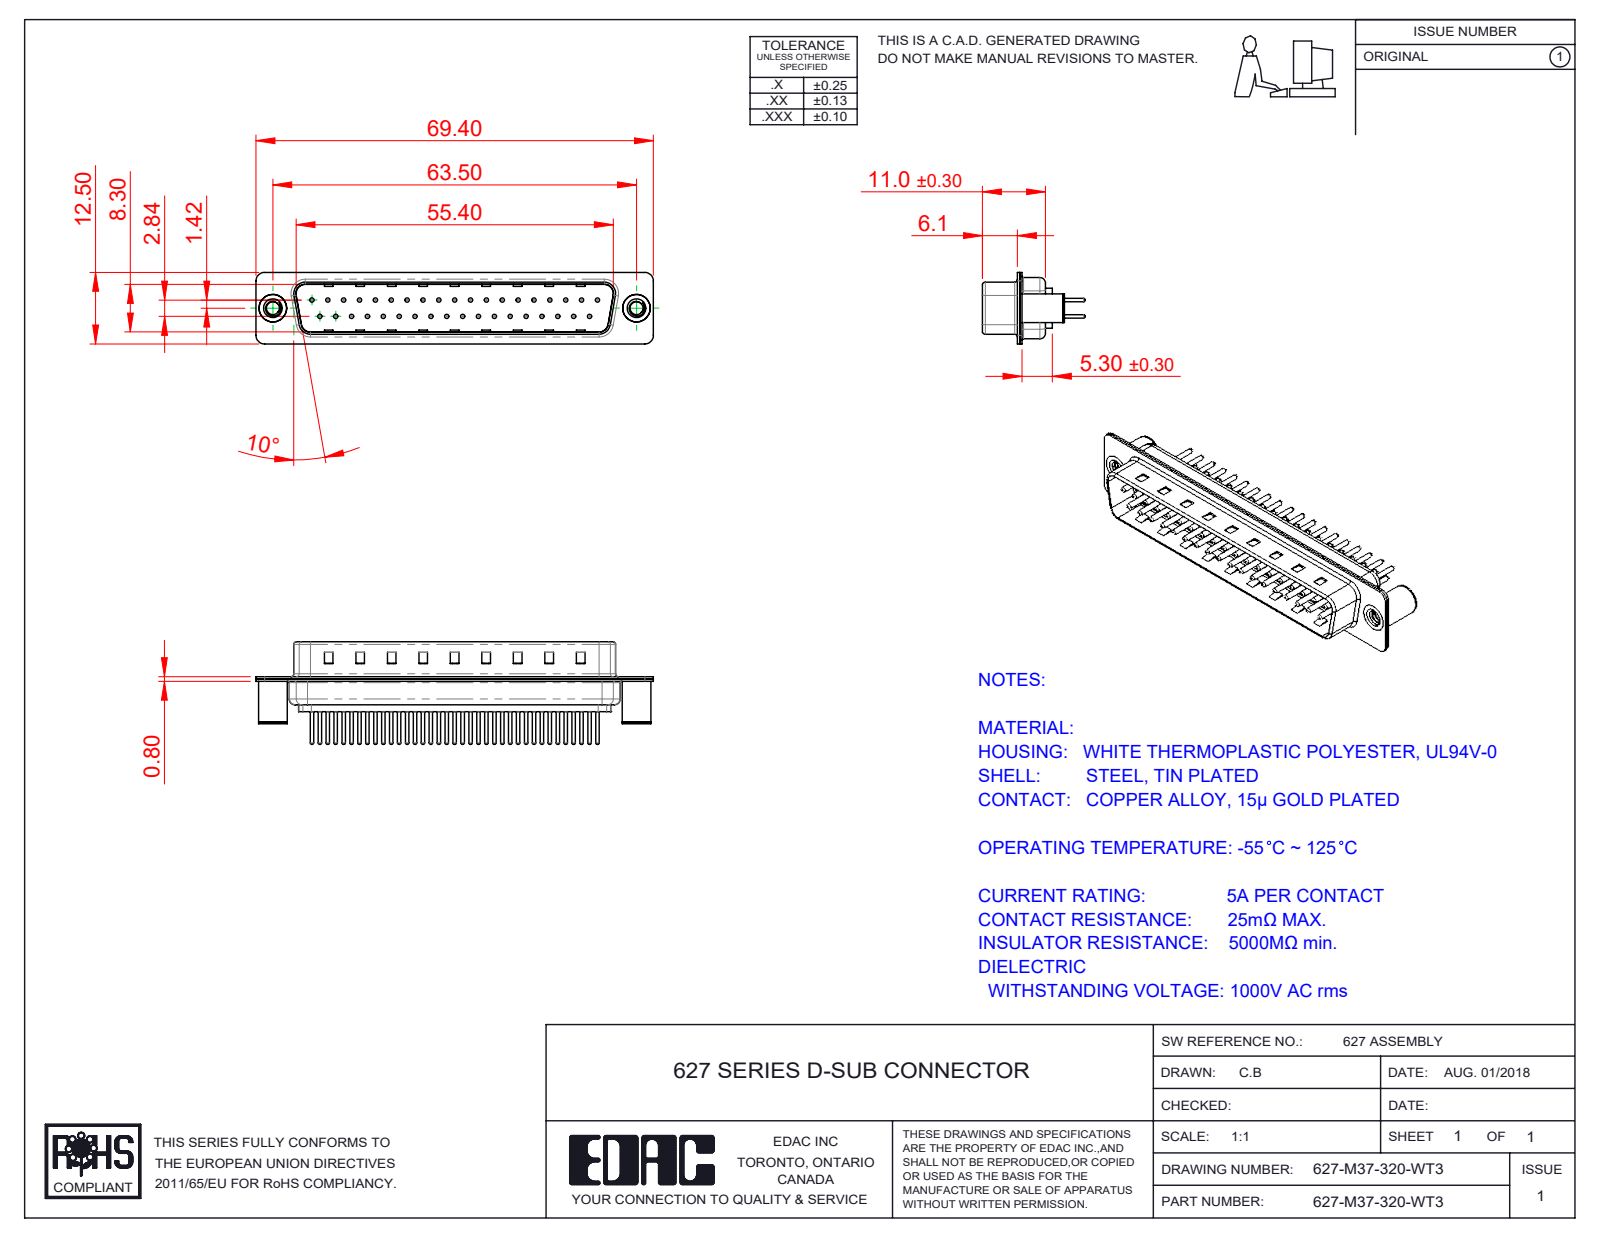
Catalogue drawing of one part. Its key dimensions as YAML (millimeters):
part_name: "627M Contact Row 1_20; 627M Shell Front_37 Contacts; 627M Contact Row 2_20; 627M Shell Rear_37 Contacts (+3 more)"
step_written_by: "SolidWorks 2020 (CONFIG_CONTROL_DESIGN)"
units: millimeters
bodies: {solids: 42, faces: 1815, planar: 462, cylindrical: 683, other: 670}
overall_size: [69.4, 17.9, 12.5]
volume: 3891
surface_area: 9528
round_holes:
  - {diameter: 0.75, count: 37}
  - {diameter: 1.6, count: 37}
  - {diameter: 2, count: 37}
  - {diameter: 2.26, count: 2}
  - {diameter: 3.26, count: 2}
  - {diameter: 4, count: 2}
  - {diameter: 4.8, count: 2}
round_bosses_or_shafts:
  - {diameter: 1.5, count: 37}
  - {diameter: 0.6, count: 37}
  - {diameter: 5, count: 2}
  - {diameter: 4.9, count: 2}
partial_cylinders:
  - {radius: 1.5, count: 16}
  - {radius: 2, count: 12}
  - {radius: 0.5, count: 8}
  - {radius: 1.6, count: 8}
  - {radius: 0.25, count: 4}
  - {radius: 0.6, count: 4}
  - {radius: 0.65, count: 4}
  - {radius: 0.9, count: 4}
face_to_face_distances: [0.4, 0.8, 9.5, 9.1, 8.7, 9.9, 1.2, 5.7, 0.75, 0.35]
hole_center_spacings: [2.77, 5.54, 3.16, 8.31, 11.08, 13.85, 16.62, 19.39]
